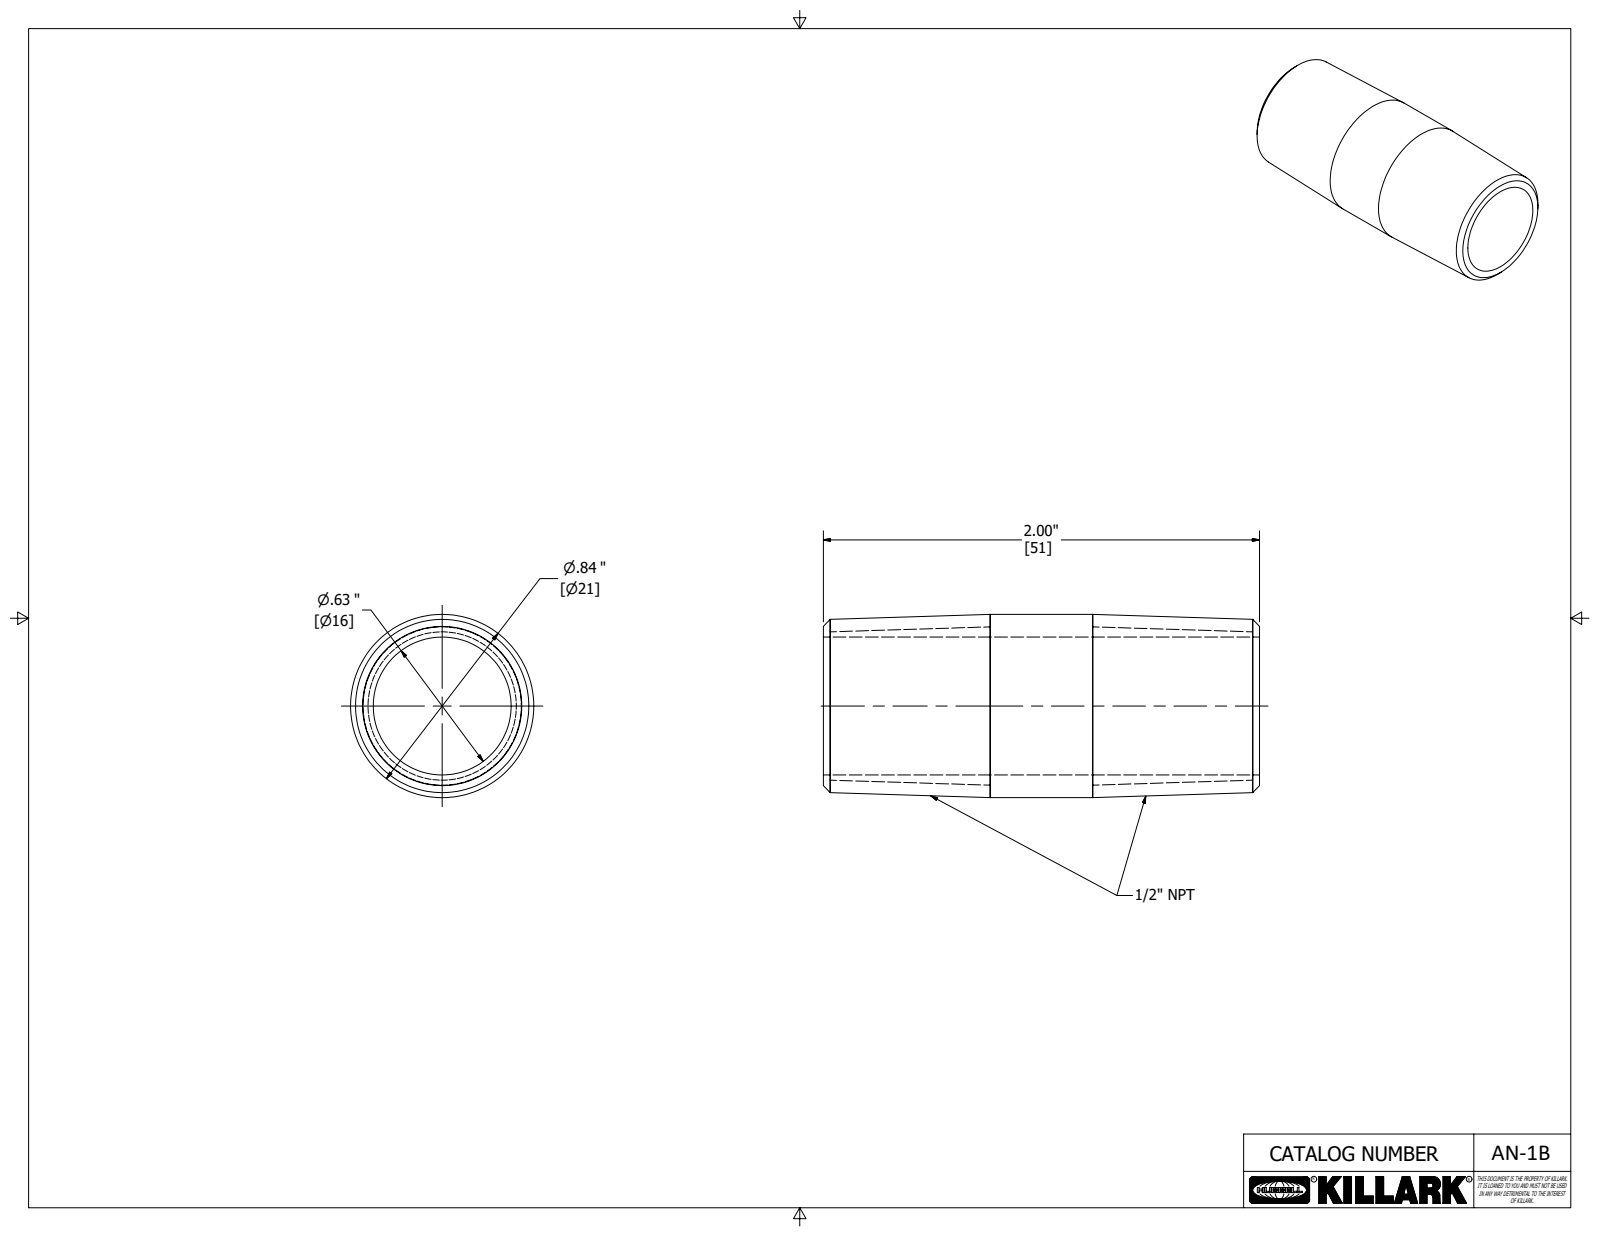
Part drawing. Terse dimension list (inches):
name: 14077-11
written by: Autodesk Inventor 2020 (AUTOMOTIVE_DESIGN)
unit: in
bodies: 1 solid, 8 faces (2 planar, 2 cylindrical, 4 other)
size: 2 × 0.84 × 0.84
volume: 0.431 in³; area: 9.404 in²
holes: 1× ⌀0.632
bosses: 1× ⌀0.84
face distances: 2
